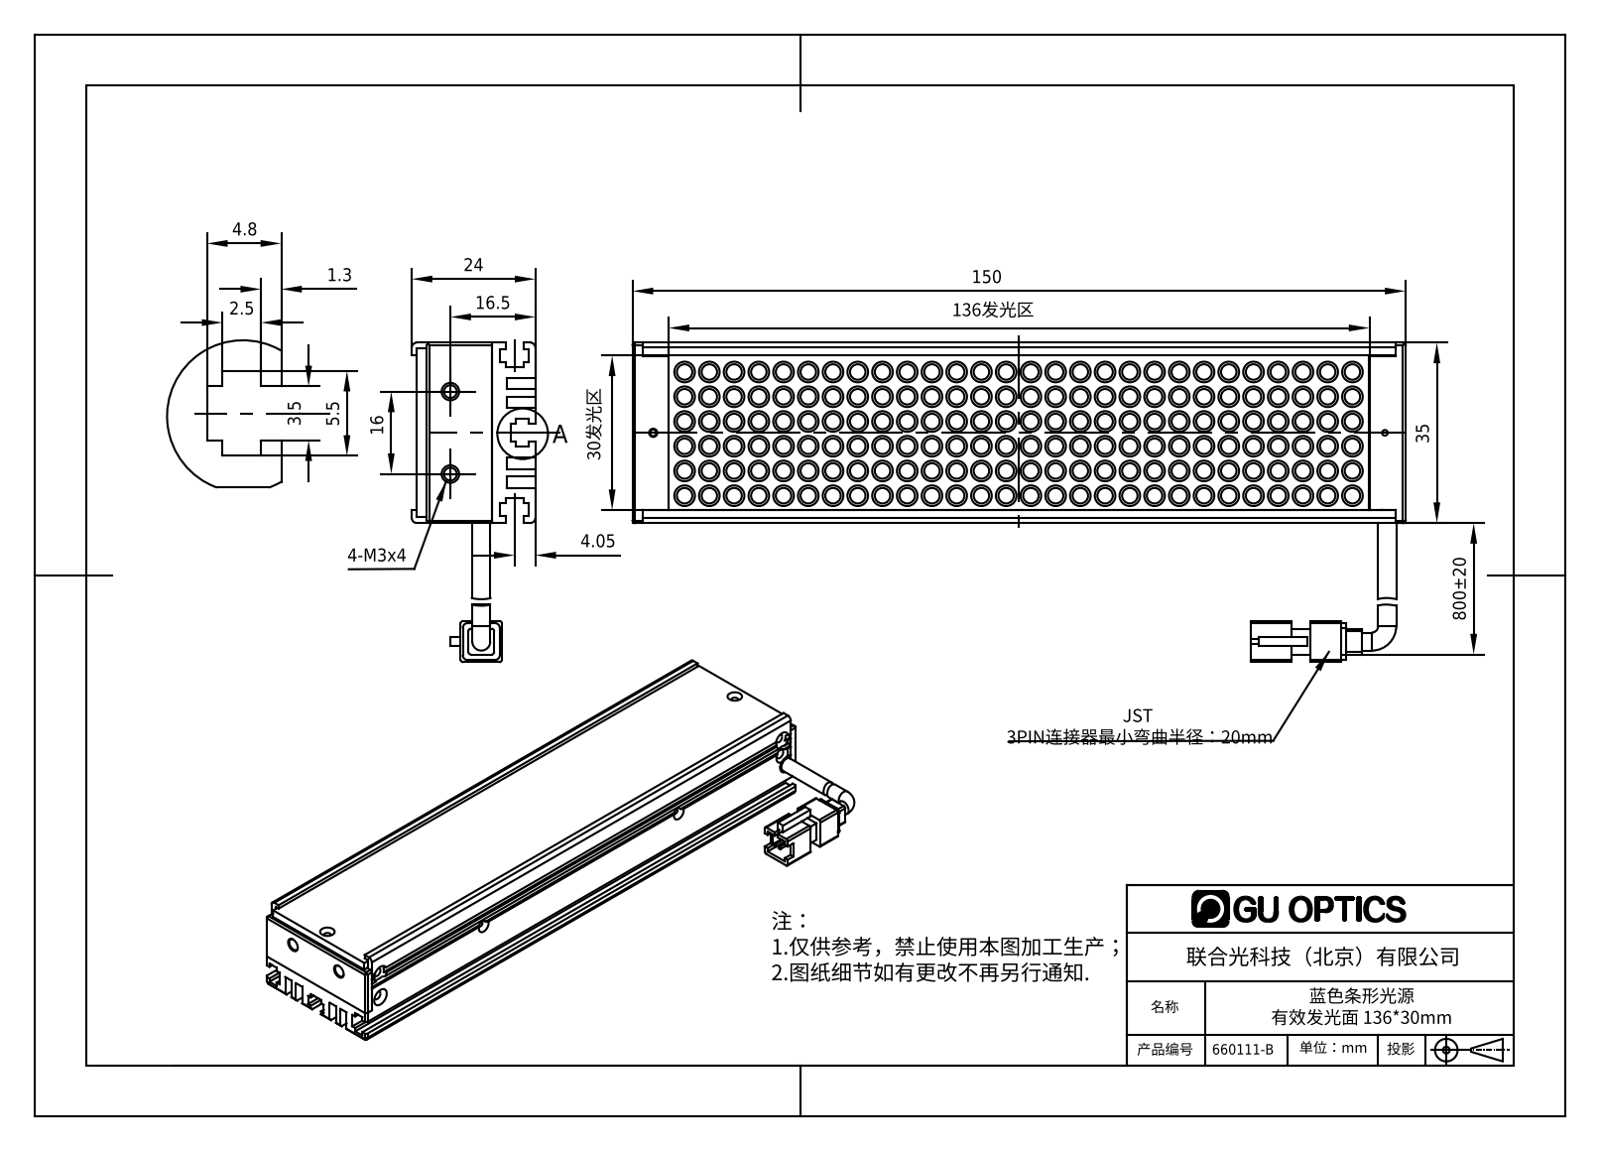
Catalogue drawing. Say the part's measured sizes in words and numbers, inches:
The part is named "660111-B". Its 3-D file was written by "SolidWorks 2016 (AUTOMOTIVE_DESIGN)". It is 8 solids with 1543 faces: 480 planar, 765 cylindrical and 298 other. Overall it measures 5.906 by 2.441 by 0.945 inches. Its volume is 4.04 cubic inches and its surface area 106 square inches. Round holes: 5 of diameter 0.063, 4 of diameter 0.049, 4 of diameter 0.087, 2 of diameter 0.067, 2 of diameter 0.098, 2 of diameter 0.118, 1 of diameter 0.094. Round bosses or shafts: 168 of diameter 0.157, 168 of diameter 0.118, 2 of diameter 0.138. Partial cylindrical surfaces (rounded edges, fillets, slot ends): 12 of radius 0.039, 8 of radius 0.02, 1 of radius 0.065. The main face-to-face distances are 0.472, 0.335, 0.079, 0.138, 0.413, 0.551, 0.039, 0.098, 0.146, 0.61. The hole center spacings are 0.276, 1.424, 4.097, 5.512, 0.098, 0.177, 0.63, 1.417.
